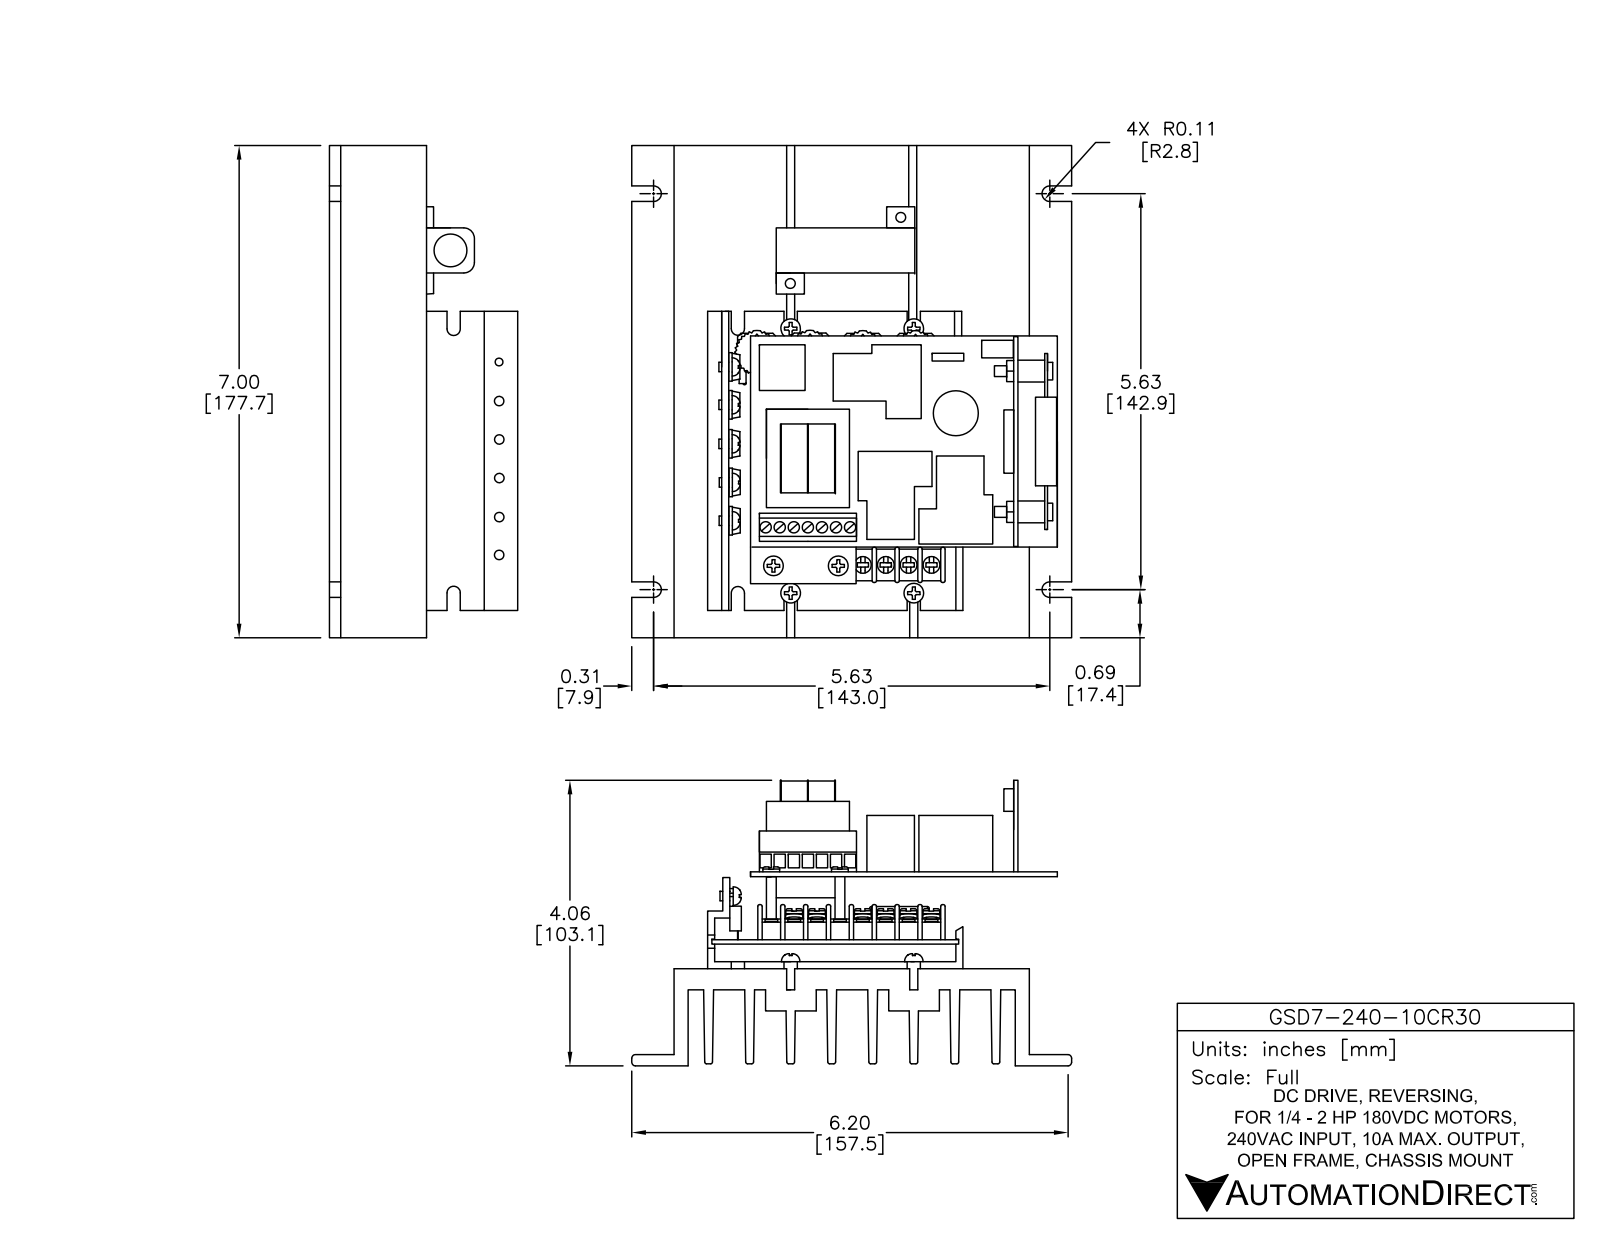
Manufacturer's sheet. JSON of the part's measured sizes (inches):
{"part_name": "TH_CAP_AXIAL_20S-16L-8D-8.2H; VARR500-890X440; TO-220AB-TYPE52; TH_CAP_AXIAL_19.050S-12L-5.25D-5.35H (+8 more)", "step_written_by": "SolidWorks 2014 (AUTOMOTIVE_DESIGN)", "units": "inches", "bodies": {"solids": 106, "faces": 5609, "planar": 3006, "cylindrical": 1961, "other": 642}, "overall_size": [7, 6.297, 3.902], "volume_in3": 34.5, "surface_area_in2": 466.7, "round_holes": [[0.033, 90], [0.043, 19], [0.035, 16], [0.046, 12], [0.07, 9], [0.035, 8], [0.09, 7], [0.147, 7], [0.04, 6], [0.11, 6], [0.144, 5], [0.111, 4]], "round_bosses_or_shafts": [[0.025, 43], [0.024, 30], [0.025, 22], [0.107, 20], [0.081, 20], [0.08, 19], [0.03, 16], [0.019, 12]], "partial_cylinders_radius": [[0.01, 25], [0.005, 23], [0.02, 12], [0.062, 12], [0.04, 11], [0.024, 10], [0.045, 8], [0.094, 8]], "face_to_face_distances": [0.585, 1.17, 2.335, 1.75, 0.3, 2.92, 3.505, 1.755, 0.1, 1.165], "hole_center_spacings": [0.2, 0.55, 0.1, 0.4, 0.461, 0.636, 0.751, 0.8]}
